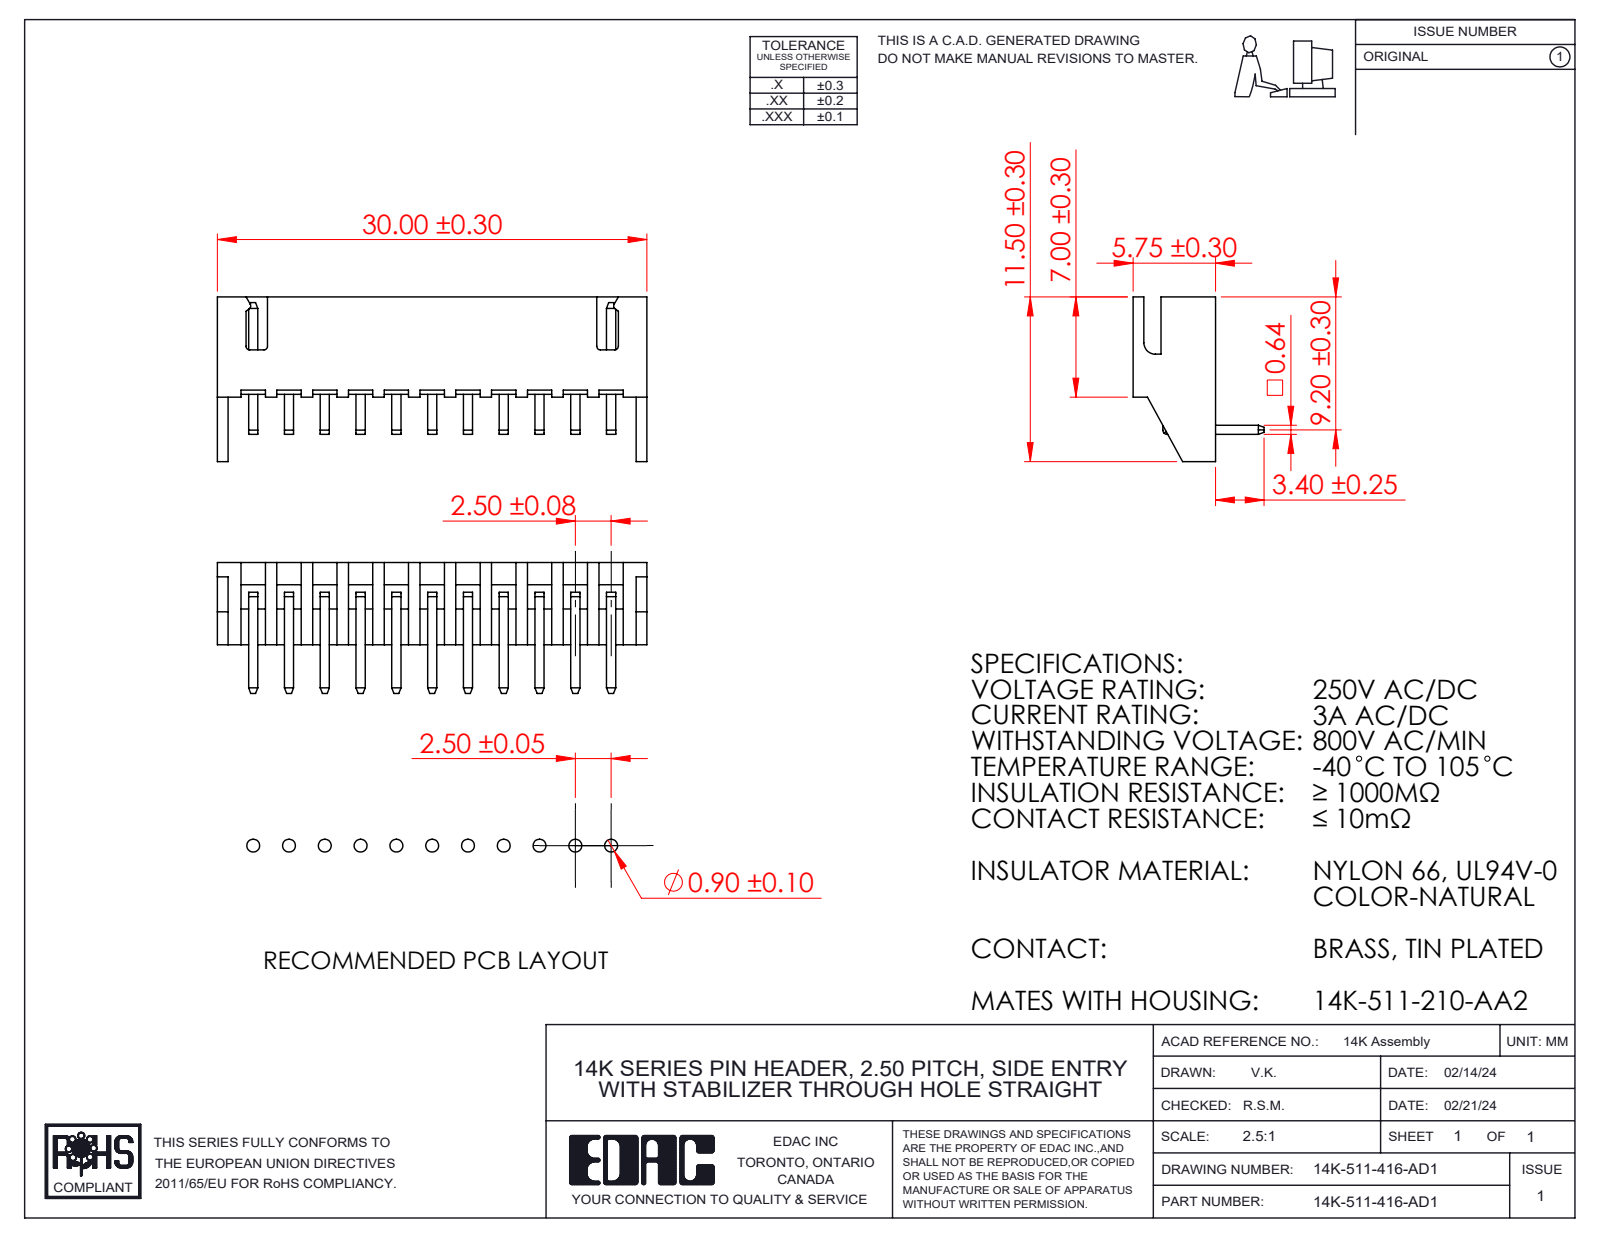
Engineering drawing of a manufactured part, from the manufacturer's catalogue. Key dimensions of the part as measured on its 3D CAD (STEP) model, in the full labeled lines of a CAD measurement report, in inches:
Part name (STEP PRODUCT): 14K-511-416-AD1; 14K Series Pin Header Insulator with Stabilizer_511; 14K Series Pin with Stabilizer_16
STEP written by: SolidWorks 2023 (CONFIG_CONTROL_DESIGN)
Units: inches
Bodies: 12 solids, 398 faces (367 planar, 31 cylindrical, 0 other)
Overall size (bounding box): 1.181 × 0.453 × 0.36
Volume: 0.037 in³ · Surface area: 2.711 in²
Partial cylindrical surfaces — rounded edges, fillets, slot ends (radius × count): R0.01 ×6, R0.012 ×2, R0.031 ×1
Main face-to-face distances: 0.197, 0.03, 0.227, 0.025, 0.167, 0.098, 0.077, 0.295, 0.394, 0.03
